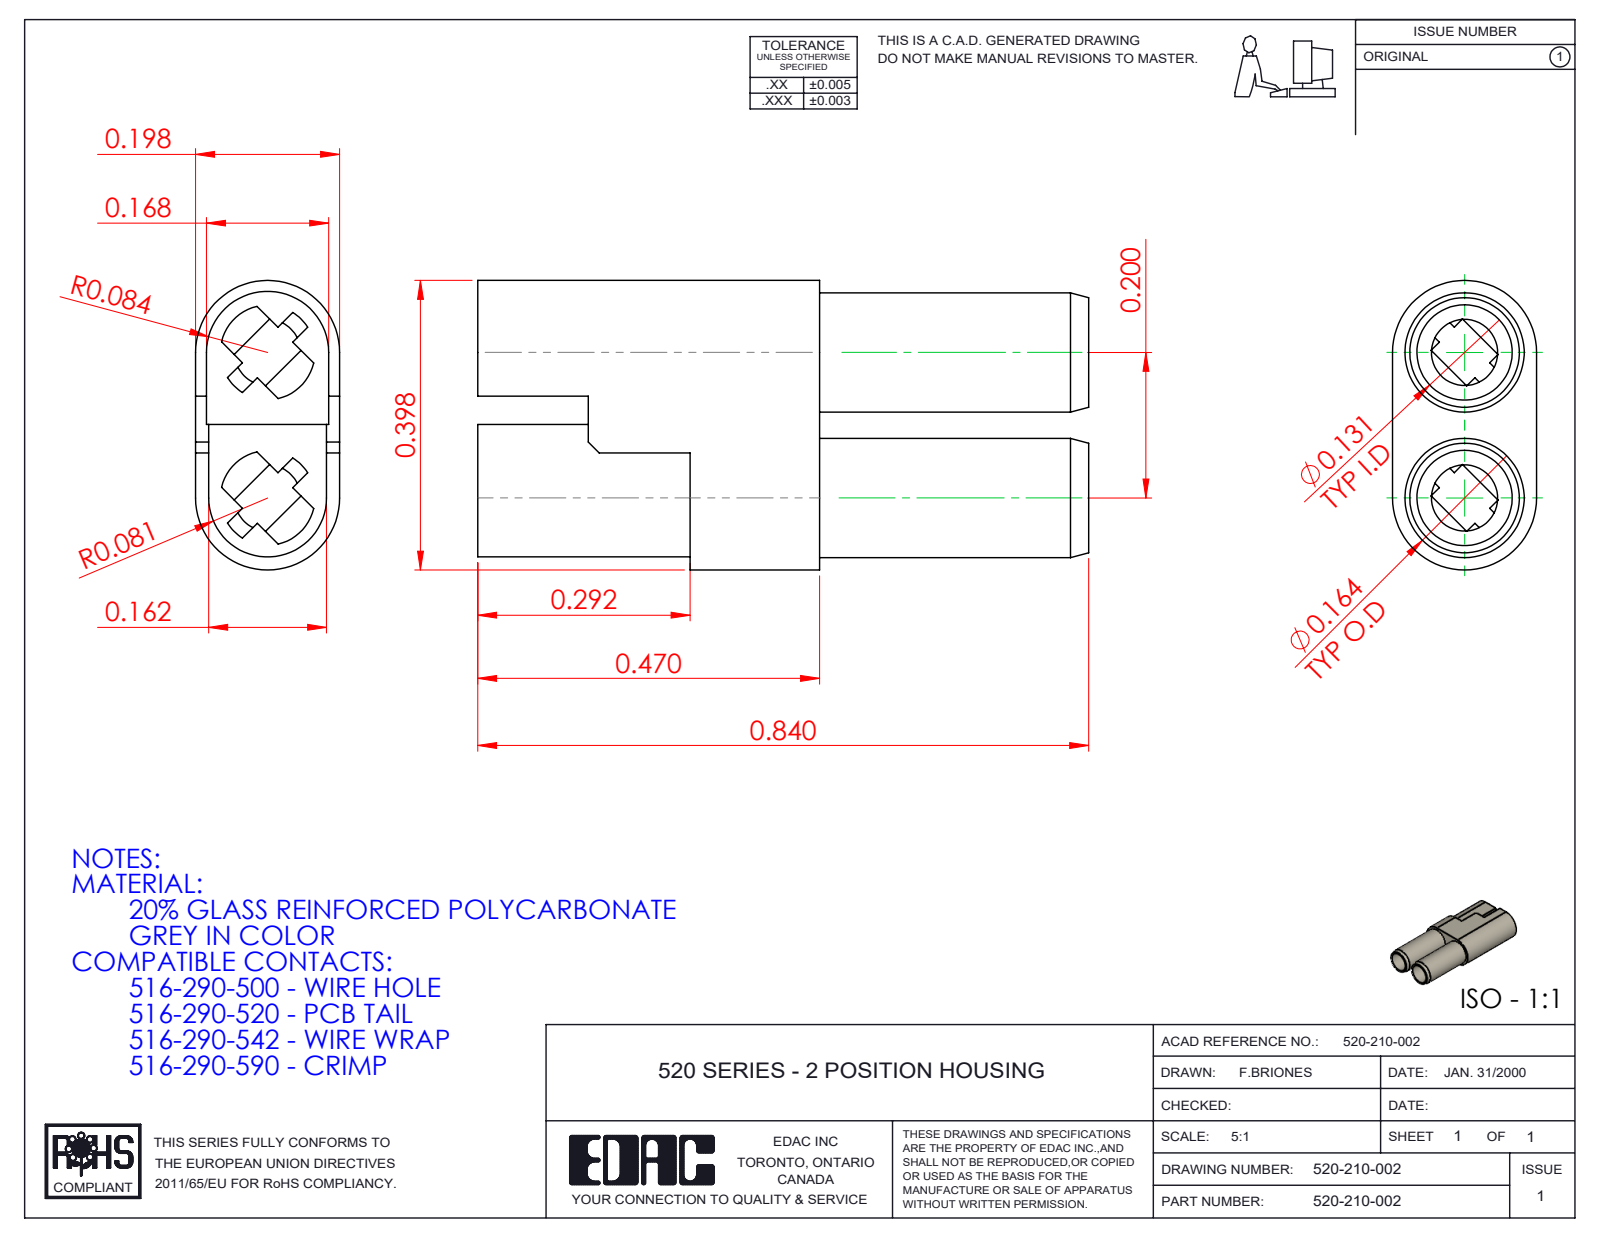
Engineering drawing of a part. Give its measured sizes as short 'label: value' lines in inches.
name: 520-210-002
written by: SolidWorks 2020 (AUTOMOTIVE_DESIGN)
unit: in
bodies: 1 solid, 92 faces (62 planar, 22 cylindrical, 8 other)
size: 0.84 × 0.398 × 0.198
volume: 0.022 in³; area: 1.731 in²
holes: 2× ⌀0.131
bosses: 2× ⌀0.164
rounds: 2× R0.065, 2× R0.099, 1× R0.081, 1× R0.084
face distances: 0.141, 0.198, 0.18, 0.069, 0.018, 0.015, 0.183, 0.165, 0.029, 0.178
hole spacings: 0.2
